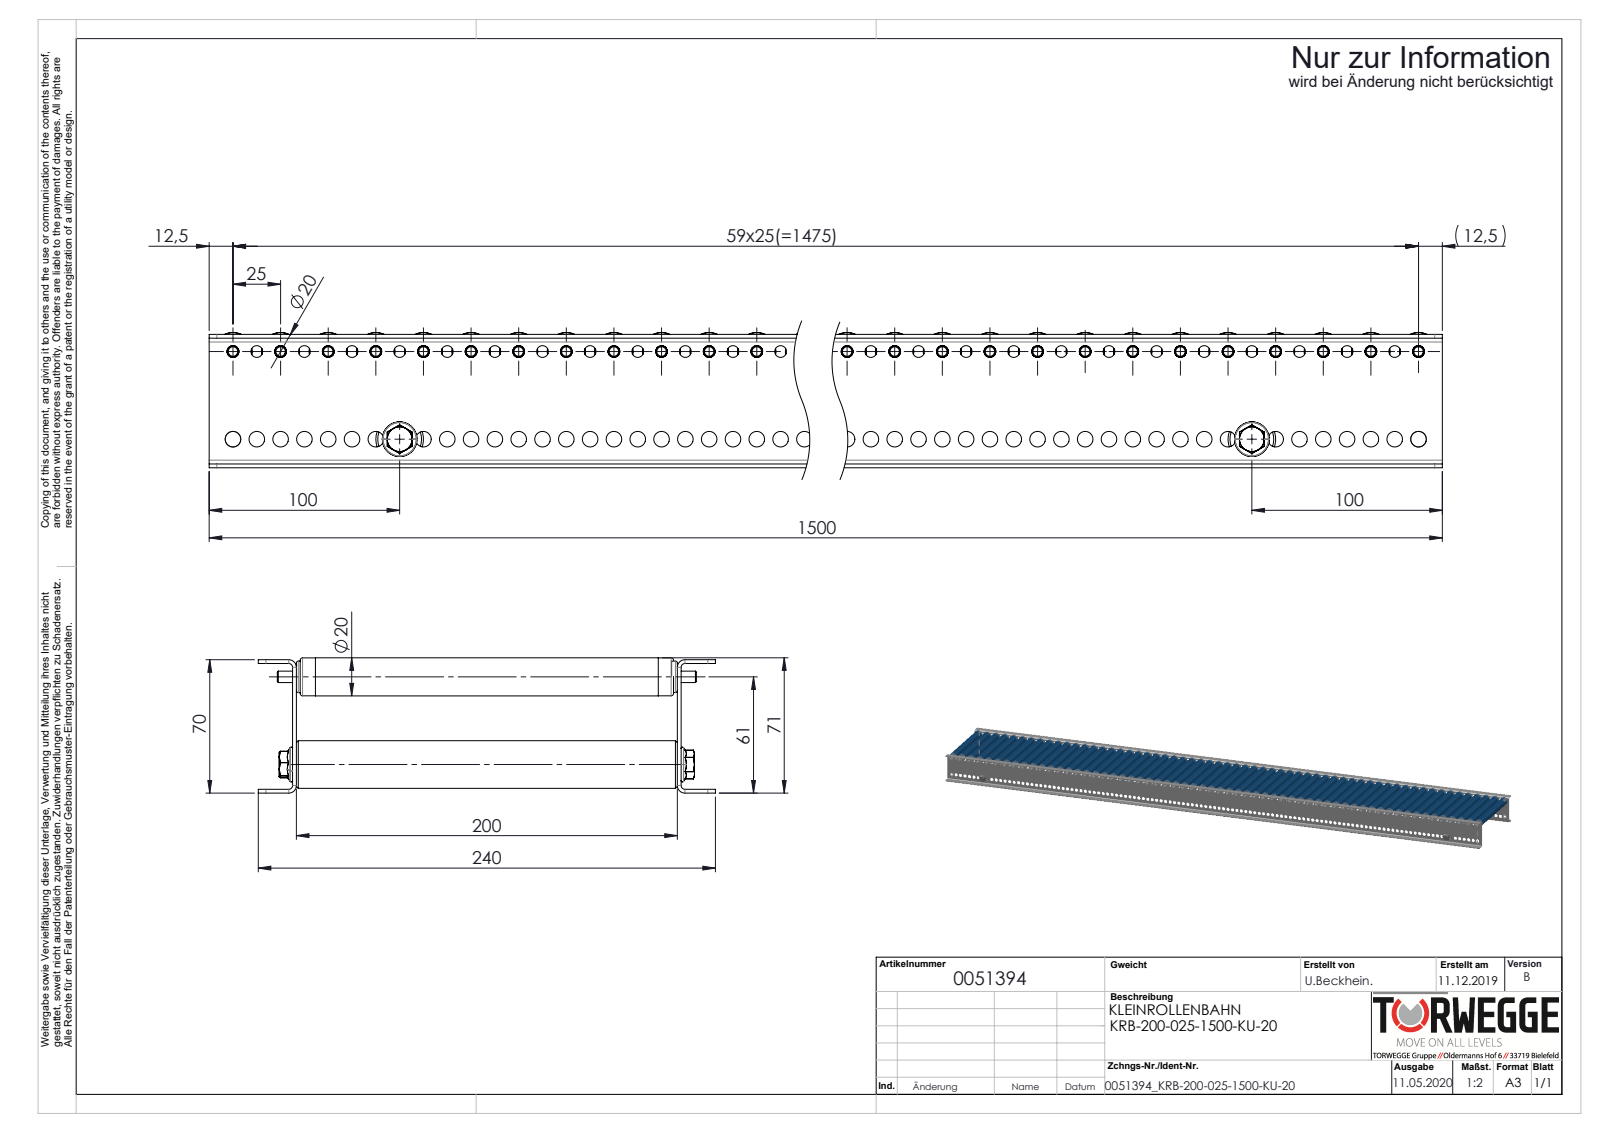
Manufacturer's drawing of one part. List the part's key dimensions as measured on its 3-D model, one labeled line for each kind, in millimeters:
Part name (STEP PRODUCT): Traversen_KFG_L200; 0051394; KUT50-20x1,5-KU-A6_FA-EL=KFG_L=200; S100994_Sperrzahnschraube_M08x16-8.8-A2K (+4 more)
STEP written by: SolidWorks 2020 (AUTOMOTIVE_DESIGN)
Units: millimetres
Bodies: 372 solids, 15860 faces (5272 planar, 5916 cylindrical, 4672 other)
Overall size (bounding box): 1500 × 240 × 71
Volume: 2 519 000 mm³ · Surface area: 2 693 000 mm²
Round holes (diameter × count): ⌀6.2 ×119, ⌀8.2 ×119, ⌀6.1 ×60, ⌀12.4 ×60, ⌀13.2 ×60, ⌀14.6 ×60, ⌀16.2 ×60, ⌀17 ×60, ⌀17.2 ×60, ⌀6.8 ×2
Round bosses / shafts (diameter × count): ⌀20 ×60, ⌀19.9 ×60, ⌀17.1 ×60, ⌀16.8 ×60, ⌀16.5 ×60, ⌀11.4 ×60, ⌀11.1 ×60, ⌀10.2 ×60
Partial cylindrical surfaces — rounded edges, fillets, slot ends (radius × count): R4.05 ×60, R4 ×8, R2 ×4
Main face-to-face distances: 2, 202, 68, 200, 204, 70, 66, 192, 10, 12
Hole centre spacings: 12.5, 25, 37.5, 50, 62.5, 75, 87.5, 100
